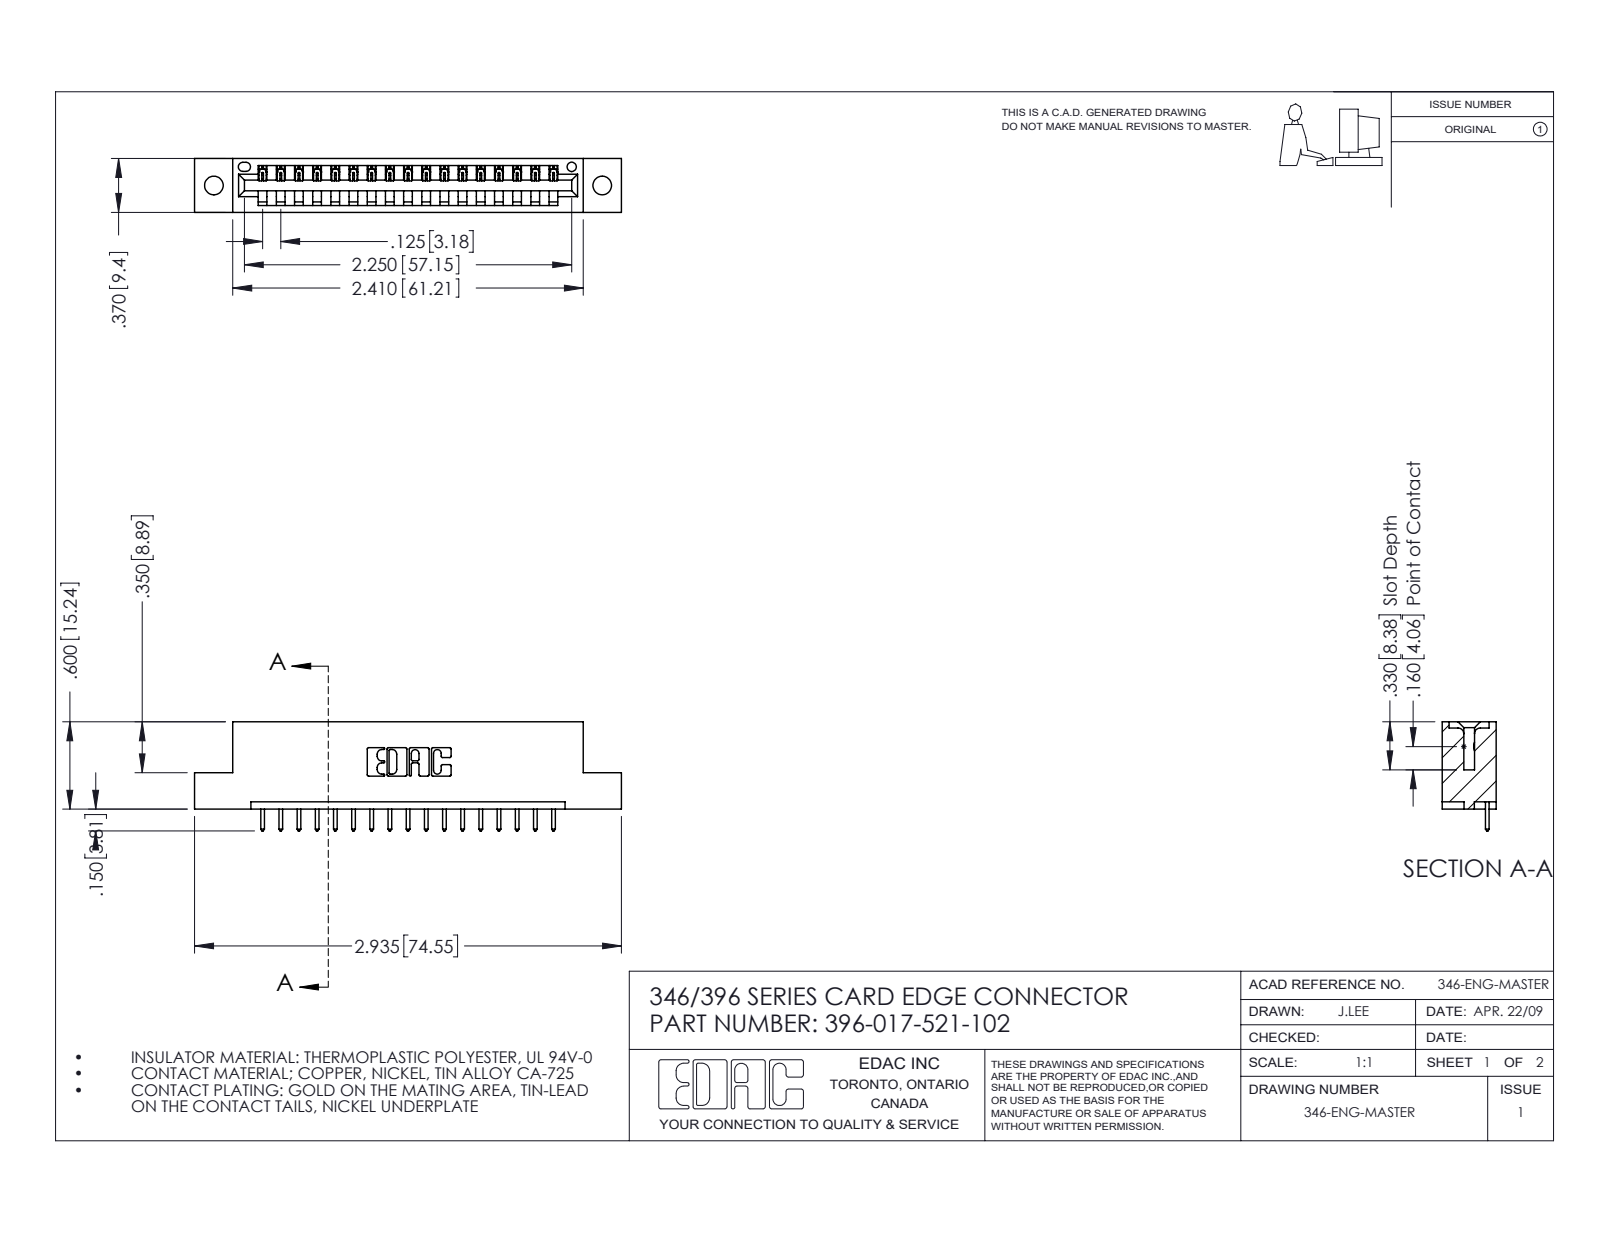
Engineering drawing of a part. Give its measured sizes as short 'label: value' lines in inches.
name: 345-292-001_345-293-121; 396-017-521-102; 346 Part_Flush Mounting Lugs - 0.128 Dia
written by: SolidWorks 2016 (CONFIG_CONTROL_DESIGN)
unit: in
bodies: 18 solids, 1108 faces (756 planar, 352 cylindrical, 0 other)
size: 2.935 × 0.75 × 0.37
volume: 0.42 in³; area: 12.19 in²
holes: 2× ⌀0.128, 1× ⌀0.064
rounds: 34× R0.006, 34× R0.01, 22× R0.01, 6× R0.007, 6× R0.031, 3× R0.026, 2× R0.031, 2× R0.04
face distances: 0.048, 0.322, 0.25, 0.37, 0.072, 0.298, 0.025, 0.148, 0.222, 0.1
hole spacings: 0.246, 2.463, 2.67
